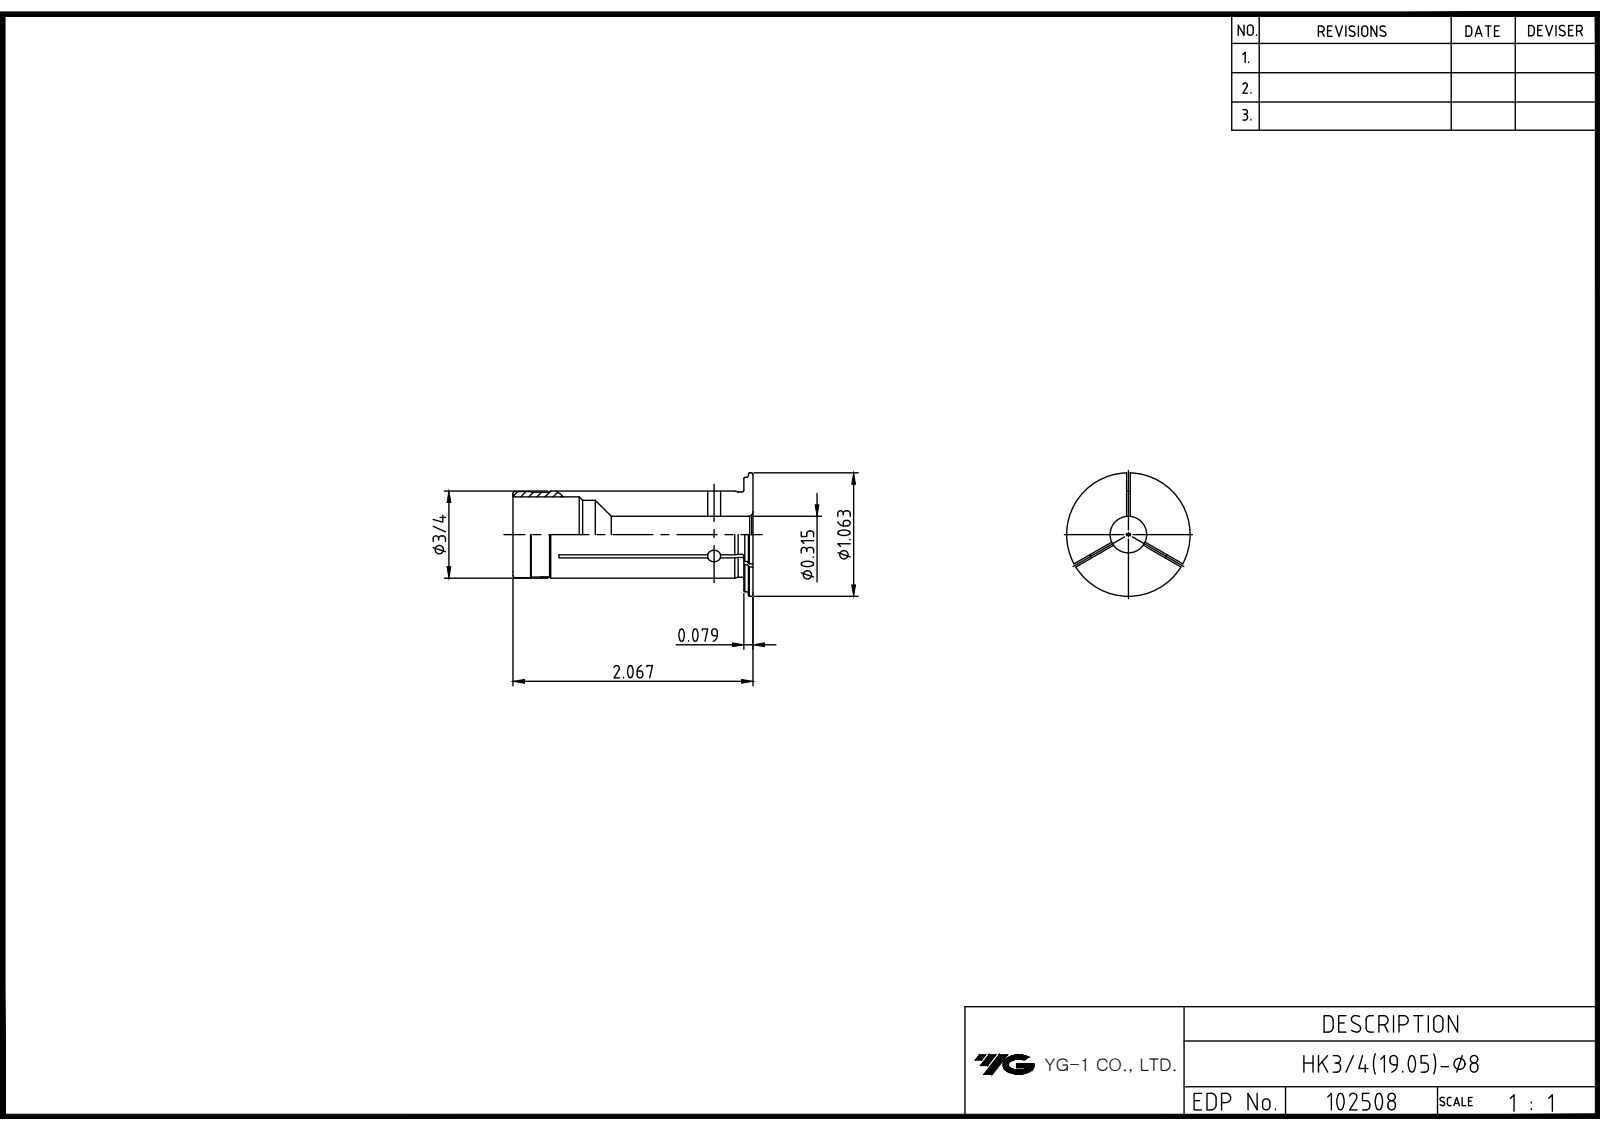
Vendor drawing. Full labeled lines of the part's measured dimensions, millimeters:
Part name (STEP PRODUCT): HK19.05-8
STEP written by: Autodesk Inventor 2022 (AUTOMOTIVE_DESIGN)
Units: millimetres
Bodies: 1 solid, 29 faces (4 planar, 9 cylindrical, 16 other)
Overall size (bounding box): 52.5 × 27 × 27
Volume: 9 673 mm³ · Surface area: 5 873 mm²
Round holes (diameter × count): ⌀8 ×1, ⌀15 ×1, ⌀16.5 ×1
Round bosses / shafts (diameter × count): ⌀27 ×1, ⌀25 ×1, ⌀19.05 ×1, ⌀18.85 ×1, ⌀18.65 ×1, ⌀18.55 ×1
Main face-to-face distances: 2, 1, 50.5, 51.5, 52.5
